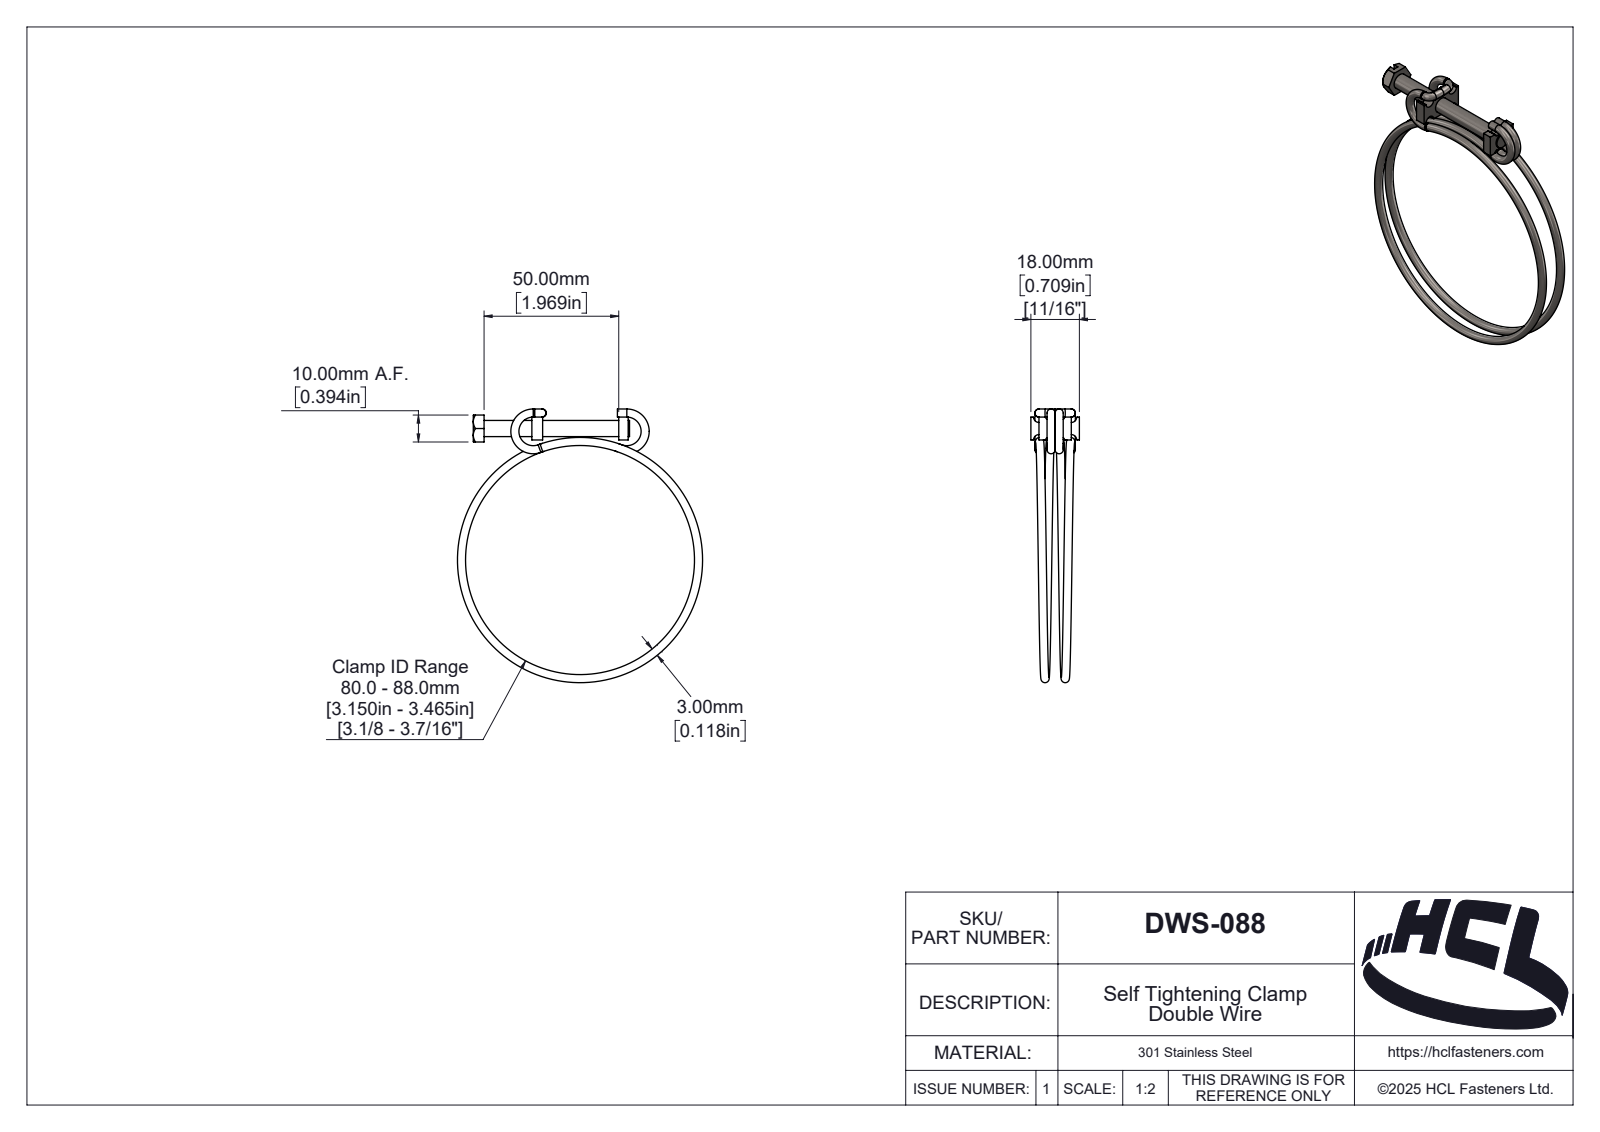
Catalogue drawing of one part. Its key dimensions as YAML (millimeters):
part_name: "DWS-088"
step_written_by: "SolidWorks 2025 (AUTOMOTIVE_DESIGN)"
units: millimeters
bodies: {solids: 6, faces: 213, planar: 55, cylindrical: 74, other: 84}
overall_size: [101.55, 91, 18]
volume: 7617
surface_area: 9159
round_holes:
  - {diameter: 6, count: 1}
round_bosses_or_shafts:
  - {diameter: 3, count: 4}
partial_cylinders:
  - {radius: 0.2, count: 12}
  - {radius: 1, count: 4}
  - {radius: 2, count: 4}
  - {radius: 0.4, count: 1}
  - {radius: 0.51, count: 1}
  - {radius: 0.53, count: 1}
  - {radius: 0.64, count: 1}
  - {radius: 0.91, count: 1}
face_to_face_distances: [4, 21.74, 10, 32.26, 3, 54, 31.76, 53.5, 1, 35.76]
